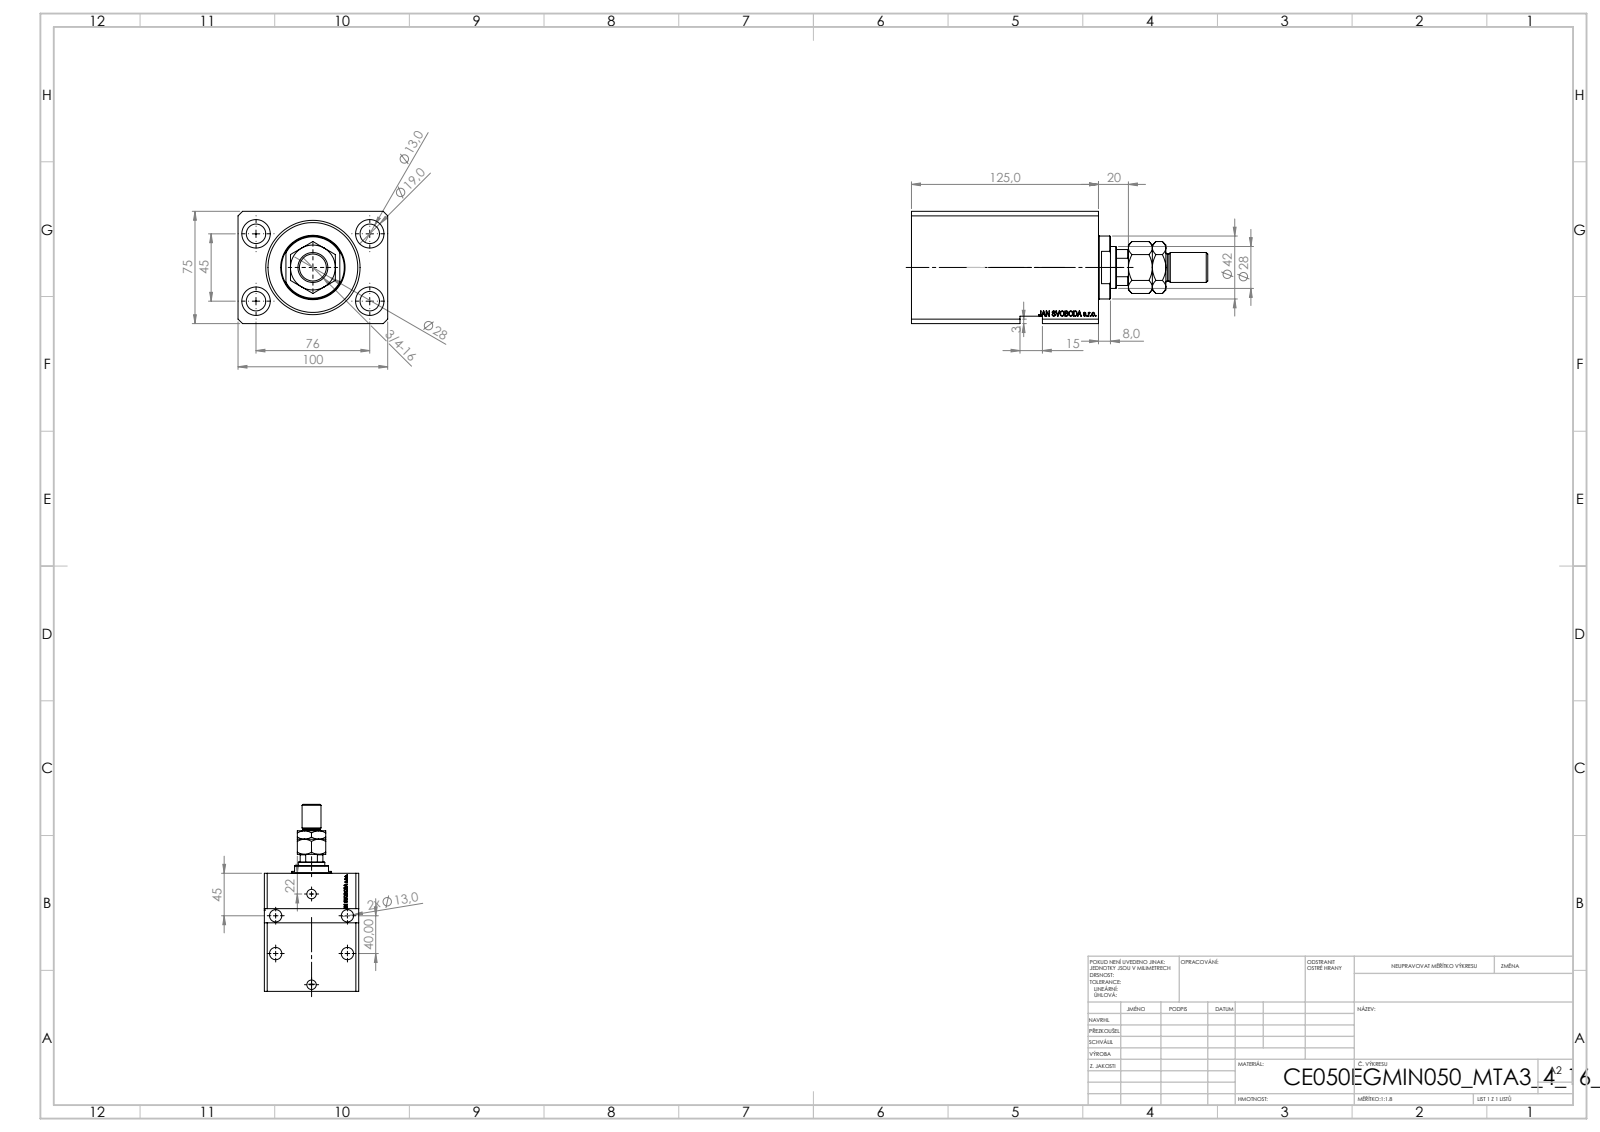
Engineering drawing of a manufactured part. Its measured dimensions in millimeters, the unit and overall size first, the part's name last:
Units: millimetres
Overall size (bounding box): 198 × 100 × 75
Round holes (diameter × count): ⌀13 ×8, ⌀1.25 ×4, ⌀19 ×4, ⌀10 ×2, ⌀13.16 ×2, ⌀20 ×2, ⌀18.5 ×1, ⌀28 ×1, ⌀50 ×1, ⌀63 ×1
Round bosses / shafts (diameter × count): ⌀42 ×1, ⌀20 ×1, ⌀18 ×1
Partial cylindrical surfaces — rounded edges, fillets, slot ends (radius × count): R13.5 ×1
Main face-to-face distances: 75, 100, 125, 20, 11.9, 113.1, 105, 93.1, 70, 13
Hole centre spacings: 44.16, 76, 40, 44.42, 45, 49.98, 50.33, 73.57
Volume: 782 606 mm³ · Surface area: 144 442 mm²
Bodies: 4 solids, 987 faces (474 planar, 108 cylindrical, 405 other)
Part name (STEP PRODUCT): V250CE_VC_E; V250CE_E_Body; MTA; V250CE_C_VCP
STEP written by: SolidWorks 2019 (CONFIG_CONTROL_DESIGN)
